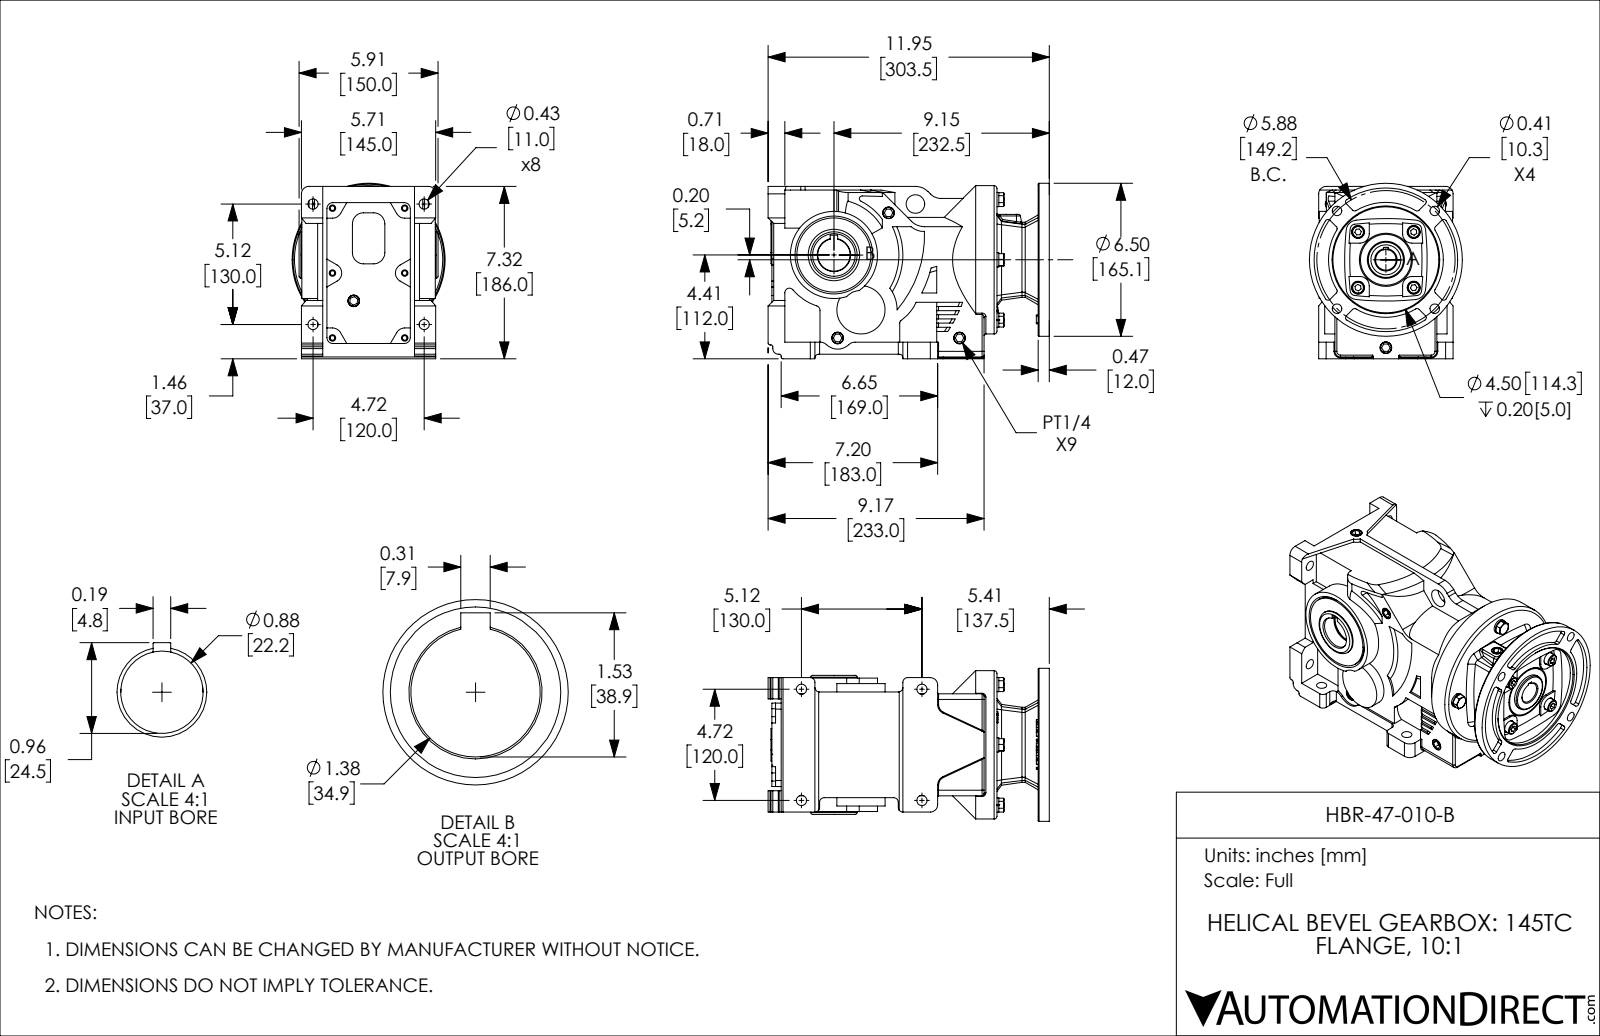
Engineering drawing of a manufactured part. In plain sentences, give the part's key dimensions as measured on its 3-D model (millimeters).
The part is named "HBR-47-010-B". Its 3-D file was written by "SolidWorks 2018 (AUTOMOTIVE_DESIGN)". It is 1 solid with 1020 faces: 497 planar, 309 cylindrical and 214 other. Overall it measures 303.5 by 189.4 by 165.1 millimeters. Its volume is 5 205 000 cubic millimeters and its surface area 322 500 square millimeters. Round holes: 8 of diameter 11, 6 of diameter 5, 6 of diameter 7, 4 of diameter 8.2, 4 of diameter 9, 4 of diameter 10.3, 4 of diameter 14, 1 of diameter 20, 1 of diameter 22.2, 1 of diameter 28, 1 of diameter 34.9, 1 of diameter 37. Round bosses or shafts: 4 of diameter 15.4, 4 of diameter 13, 4 of diameter 8, 1 of diameter 165.1, 1 of diameter 160, 1 of diameter 94, 1 of diameter 80, 1 of diameter 55. Partial cylindrical surfaces (rounded edges, fillets, slot ends): 18 of radius 3, 14 of radius 2, 14 of radius 10, 10 of radius 5, 9 of radius 12, 6 of radius 4, 5 of radius 1, 4 of radius 6.5. The main face-to-face distances are 5, 2, 110, 44.5, 287.5, 4, 3, 13, 10, 8. The hole center spacings are 46.1, 54.2, 85.9, 99.7, 129, 42.5, 130, 32.1.
